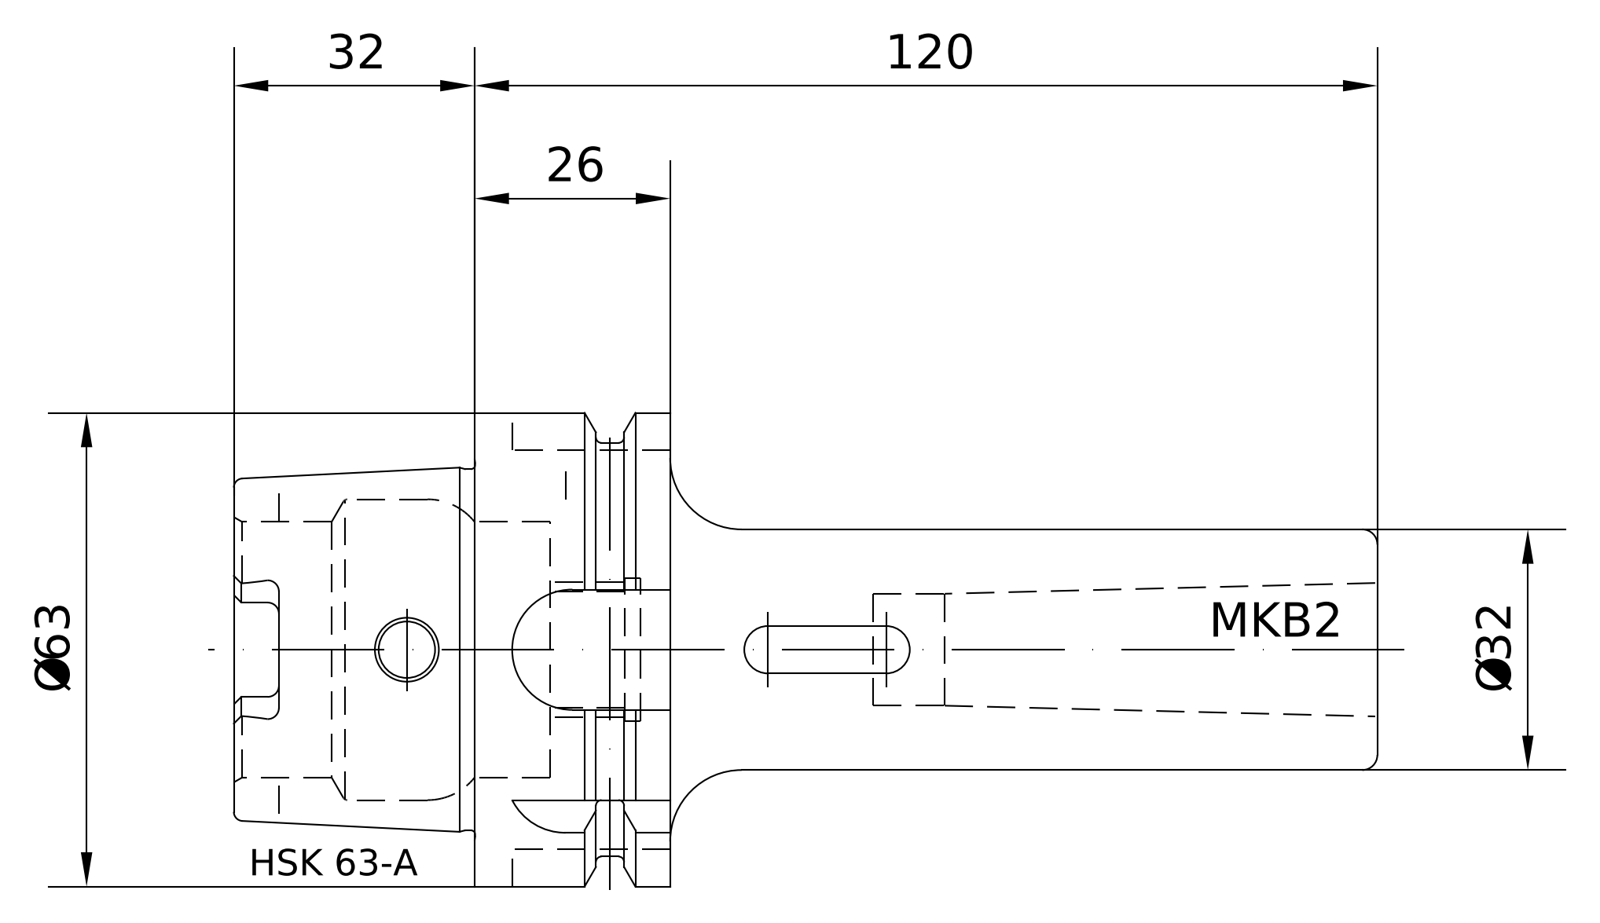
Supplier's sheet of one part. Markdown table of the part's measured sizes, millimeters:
| quantity | value |
| --- | --- |
| part name | A63-080-02 |
| STEP written by | PRO/ENGINEER BY PARAMETRIC TECHNOLOGY CORPORATION, 2010430 (CONFIG_CONTROL_DESIGN) |
| units | millimeters |
| bodies | 1 solid, 173 faces (57 planar, 48 cylindrical, 68 other) |
| overall size | 152 × 63 × 63 |
| volume | 145 682 mm³ |
| surface area | 34 889 mm² |
| round holes (diameter × count) | 7.5 × 1, 10 × 1, 14.9 × 1, 16.92 × 1, 18.32 × 1, 18.66 × 1, 34 × 1, 40 × 1 |
| round bosses / shafts (diameter × count) | 63 × 1, 55 × 1, 48.04 × 1, 32 × 1, 18 × 1 |
| partial cylindrical surfaces (radius × count) | 1.5 × 6, 3 × 4, 8 × 1, 8.02 × 1, 9.02 × 1 |
| main face-to-face distances | 26, 10, 16, 32, 120, 110, 94, 42, 58, 152 |
